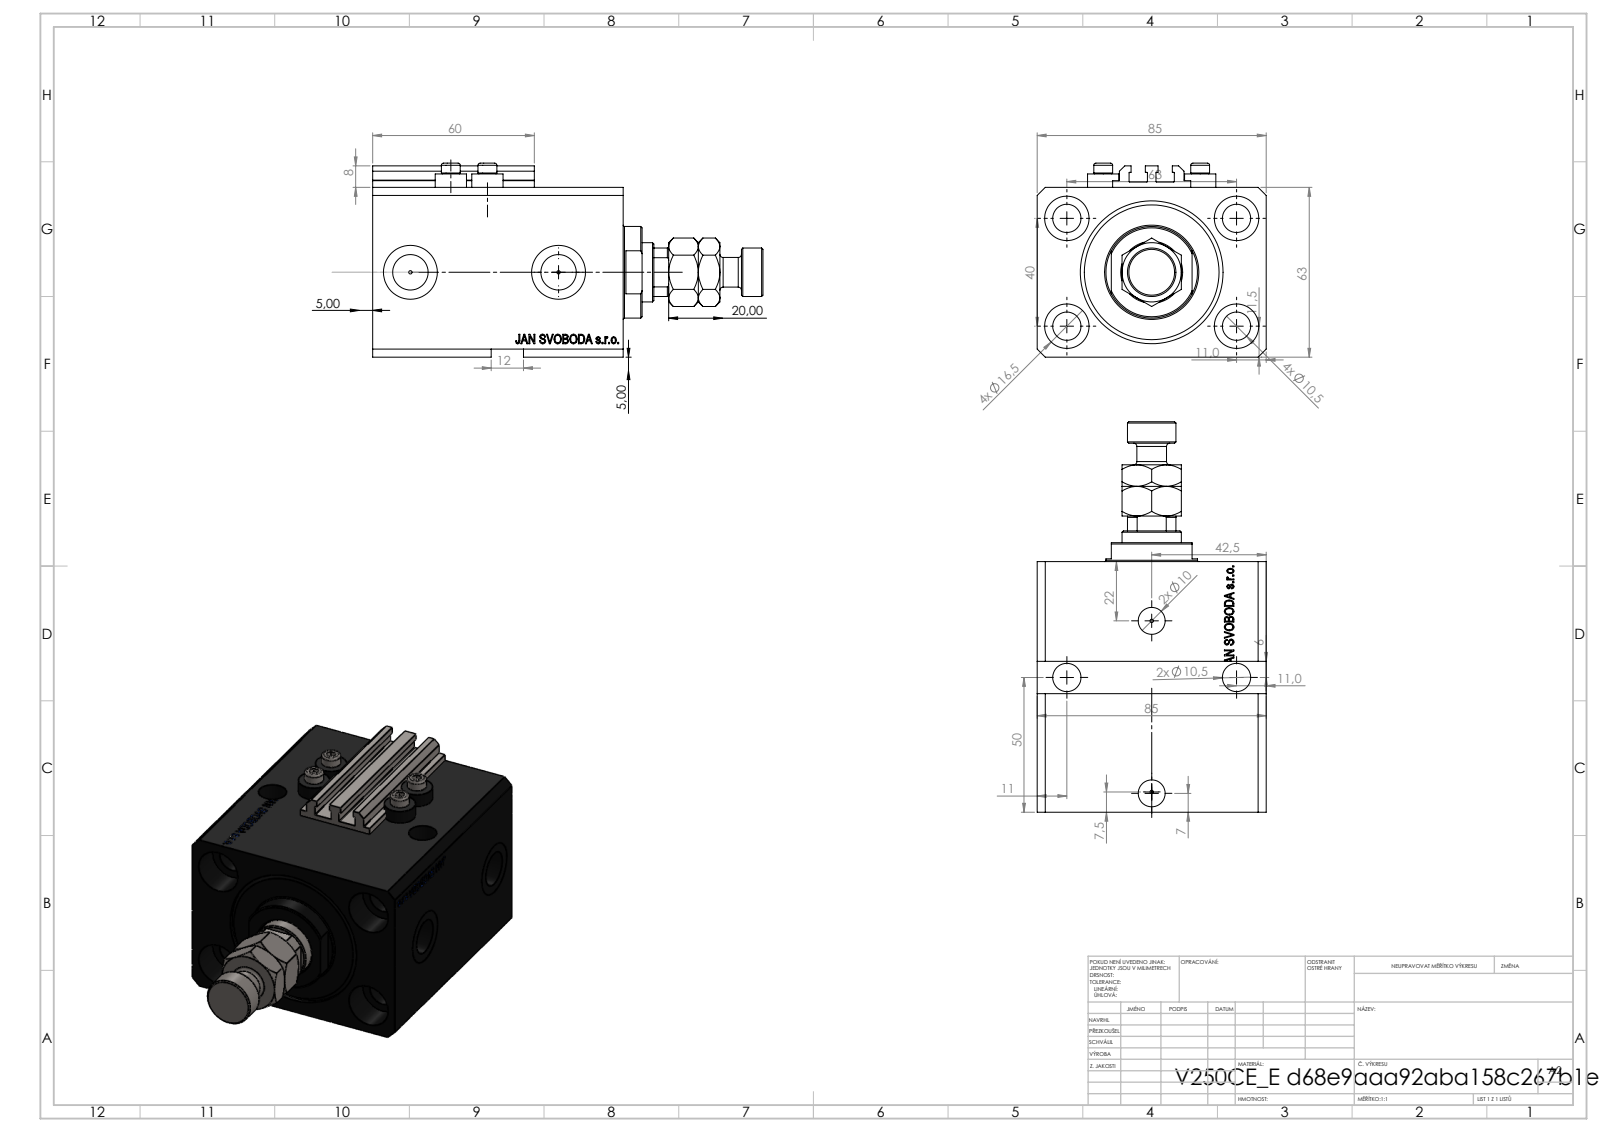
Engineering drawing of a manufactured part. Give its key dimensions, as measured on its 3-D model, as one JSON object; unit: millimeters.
{"part_name": "ALLEN BOLT V250CE; V250CE_C_VCP; V250CE_VC_E; MFA (+1 more)", "step_written_by": "SolidWorks 2019 (CONFIG_CONTROL_DESIGN)", "units": "millimeters", "bodies": {"solids": 9, "faces": 1155, "planar": 555, "cylindrical": 142, "other": 458}, "overall_size": [145, 85, 72], "volume_mm3": 444319, "surface_area_mm2": 100174, "round_holes": [[10.5, 6], [1.25, 4], [4, 4], [16.5, 4], [10, 2], [13.16, 2], [20, 2], [12.5, 1], [22, 1], [40, 1], [53, 1]], "round_bosses_or_shafts": [[11.6, 4], [7, 4], [34, 1], [18, 1], [11, 1]], "partial_cylinders_radius": [[0.2, 10], [10.5, 1]], "face_to_face_distances": [63, 85, 93, 17, 76, 11.4, 64.6, 81.6, 3, 65], "hole_center_spacings": [37.31, 63, 13.6, 15.4, 24.96, 28.02, 28.43, 33.62]}
